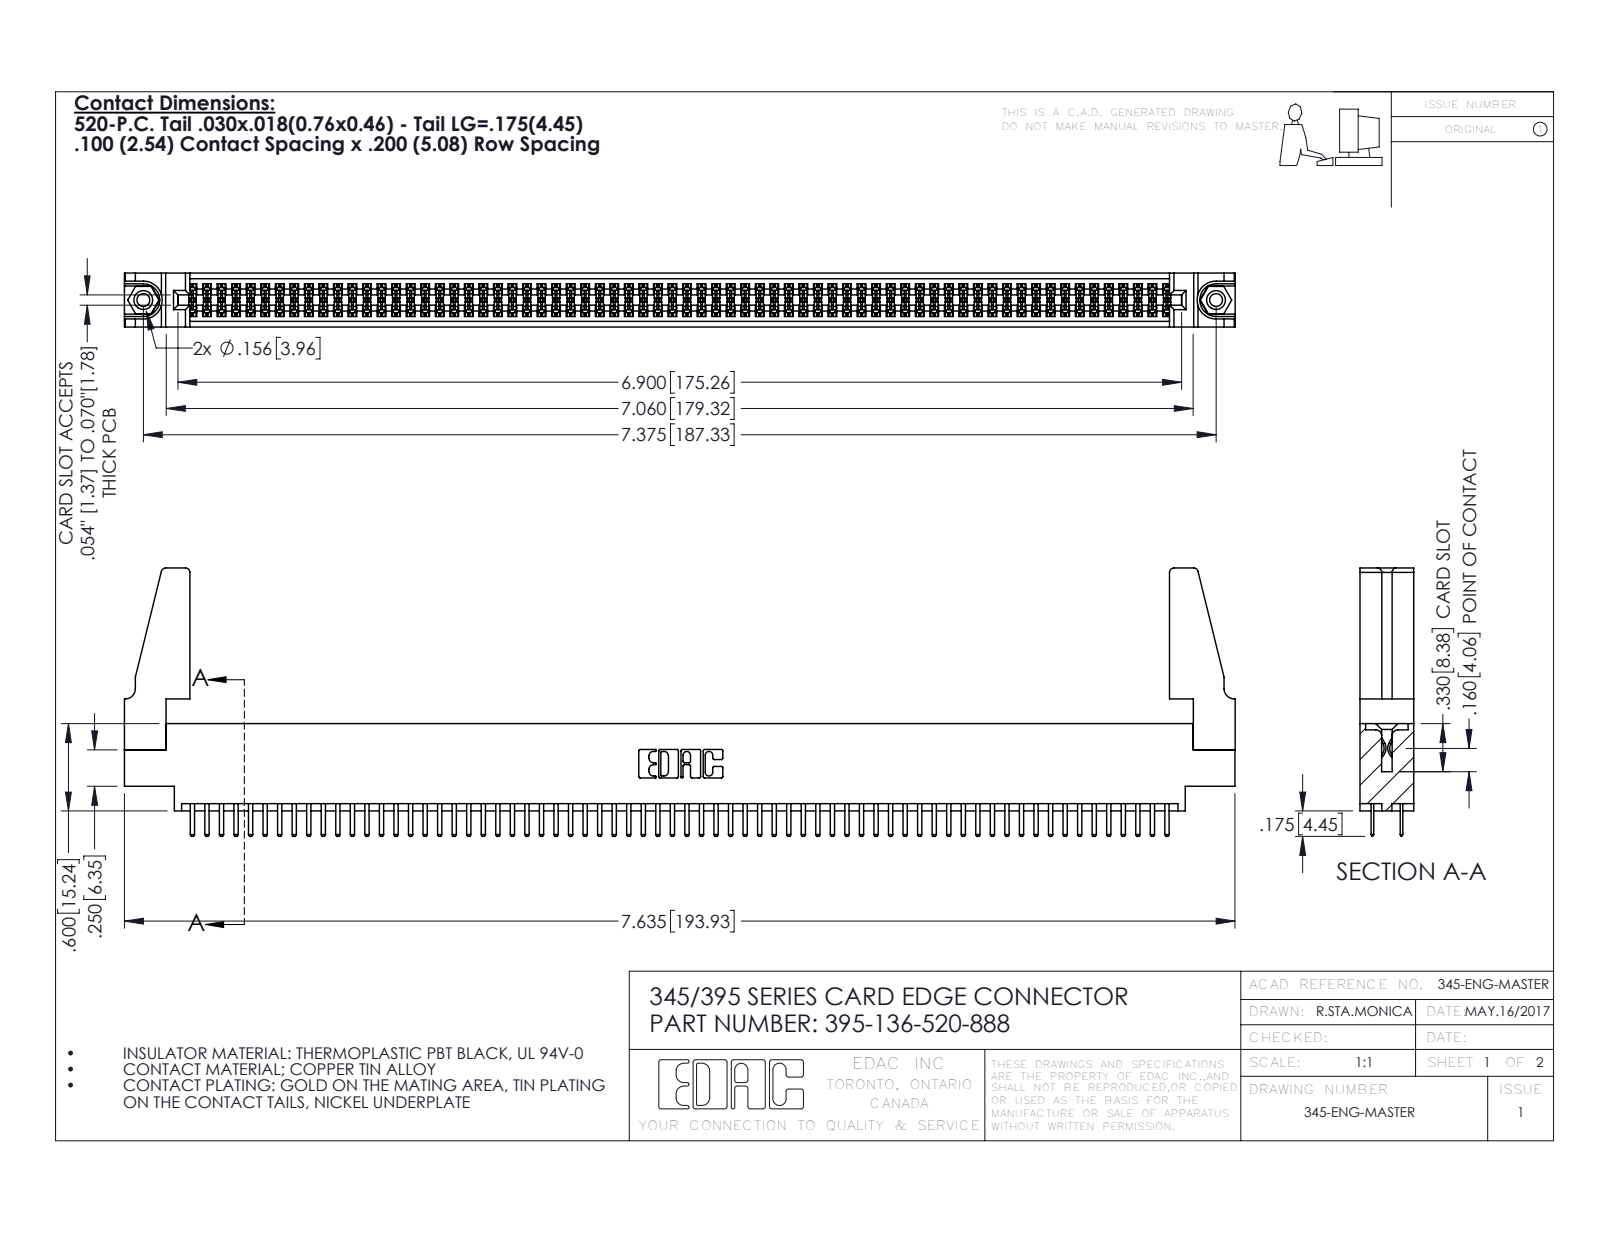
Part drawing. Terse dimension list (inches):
name: 395-136-520-888; 345 Part_0.170 Offset - 0.156 Dia-TH; 345-220-078_345-220-088; 345-250-001_345-250-001-102 (+1 more)
written by: SolidWorks 2016 (CONFIG_CONTROL_DESIGN)
unit: in
bodies: 141 solids, 7598 faces (4916 planar, 2666 cylindrical, 16 other)
size: 7.636 × 1.845 × 0.37
volume: 1.352 in³; area: 48.97 in²
holes: 2× ⌀0.089, 2× ⌀0.125, 2× ⌀0.156, 1× ⌀0.064
bosses: 2× ⌀0.155
rounds: 204× R0.006, 140× R0.01, 22× R0.01, 8× R0.03, 6× R0.007, 6× R0.031, 3× R0.026, 2× R0.014
face distances: 0.072, 0.298, 0.37, 0.2, 0.098, 0.272, 0.025, 0.225, 0.022, 0.072
hole spacings: 0.27, 7.139, 7.375
